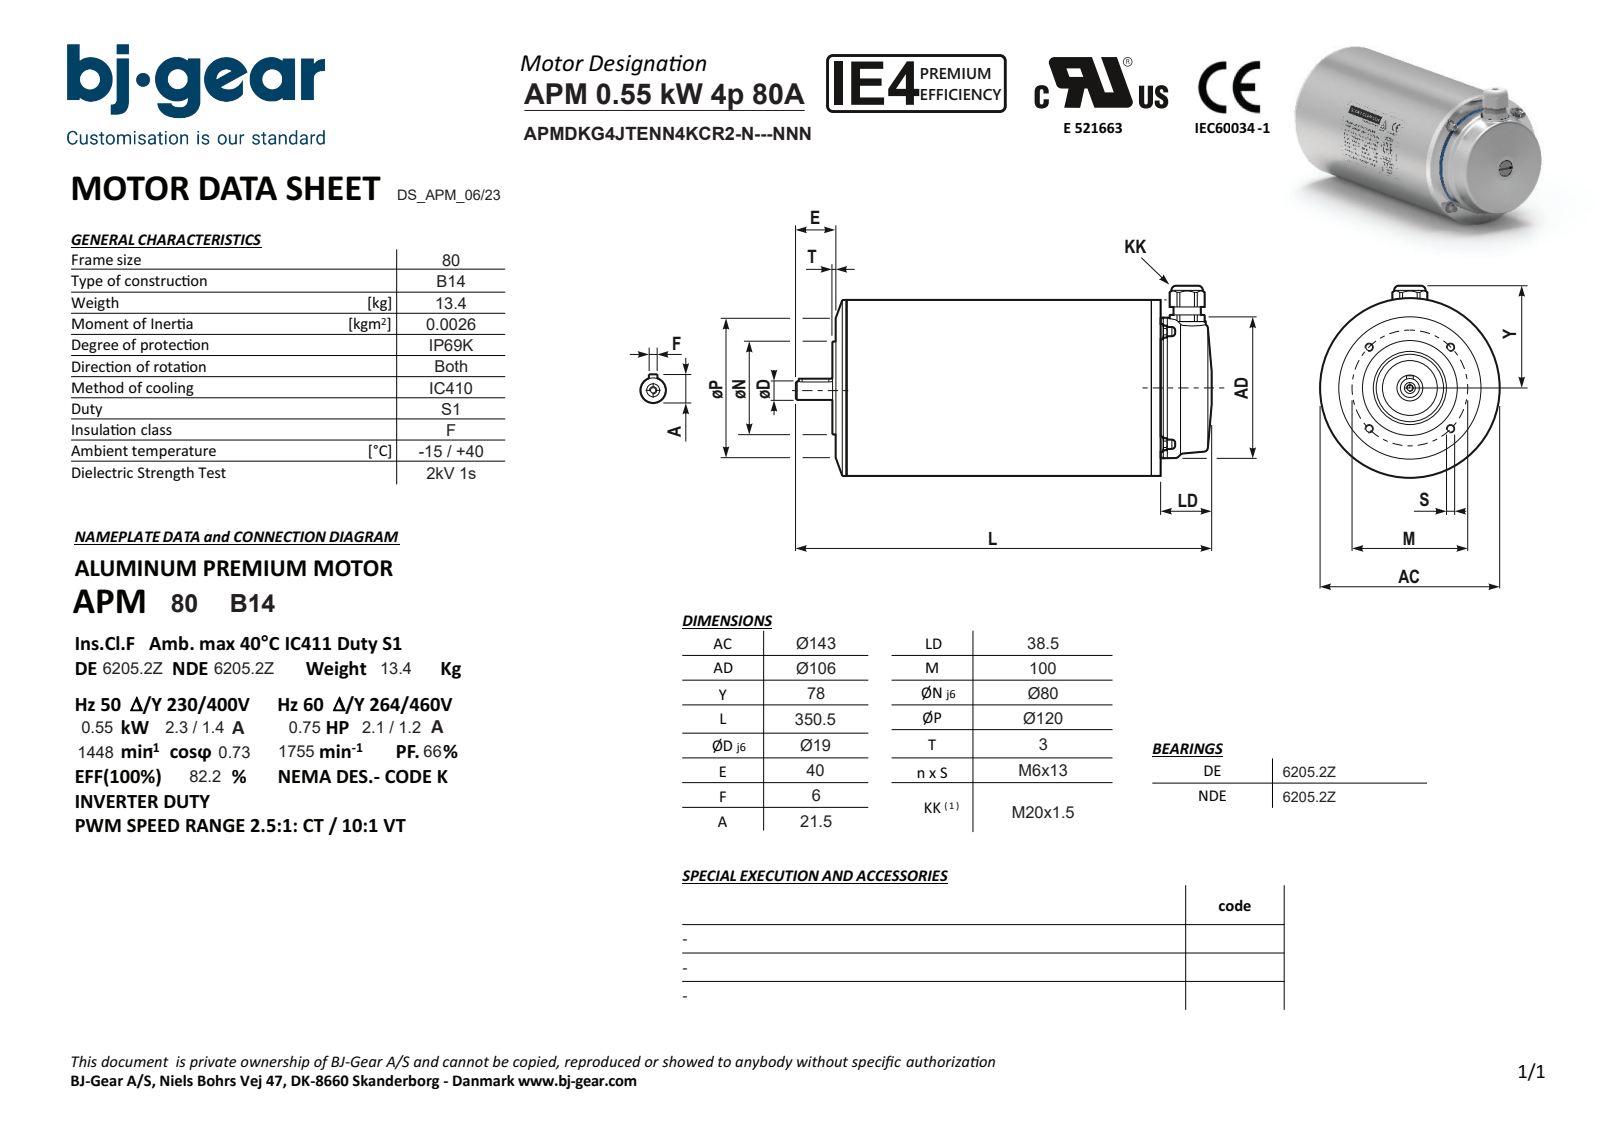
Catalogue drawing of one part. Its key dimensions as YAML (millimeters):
part_name: "APMDKG4JTENN4KCR2-N---NNN"
step_written_by: "Solid Edge (AUTOMOTIVE_DESIGN)"
units: millimeters
bodies: {solids: 1, faces: 156, planar: 75, cylindrical: 50, other: 31}
overall_size: [350.5, 148.3, 142.6]
volume: 4636000
surface_area: 172344
round_holes:
  - {diameter: 4.92, count: 5}
  - {diameter: 6.4, count: 1}
  - {diameter: 16, count: 1}
  - {diameter: 28, count: 1}
  - {diameter: 65, count: 1}
round_bosses_or_shafts:
  - {diameter: 11.5, count: 4}
  - {diameter: 7, count: 4}
  - {diameter: 142.6, count: 1}
  - {diameter: 142.6, count: 1}
  - {diameter: 106, count: 1}
  - {diameter: 80, count: 1}
  - {diameter: 25, count: 1}
  - {diameter: 23.7, count: 1}
partial_cylinders:
  - {radius: 3, count: 2}
  - {radius: 13.2, count: 1}
face_to_face_distances: [272, 6, 266, 9, 3, 275, 24, 310.5, 38.5, 304.5]
hole_center_spacings: [50.01, 70.72, 100.01]
